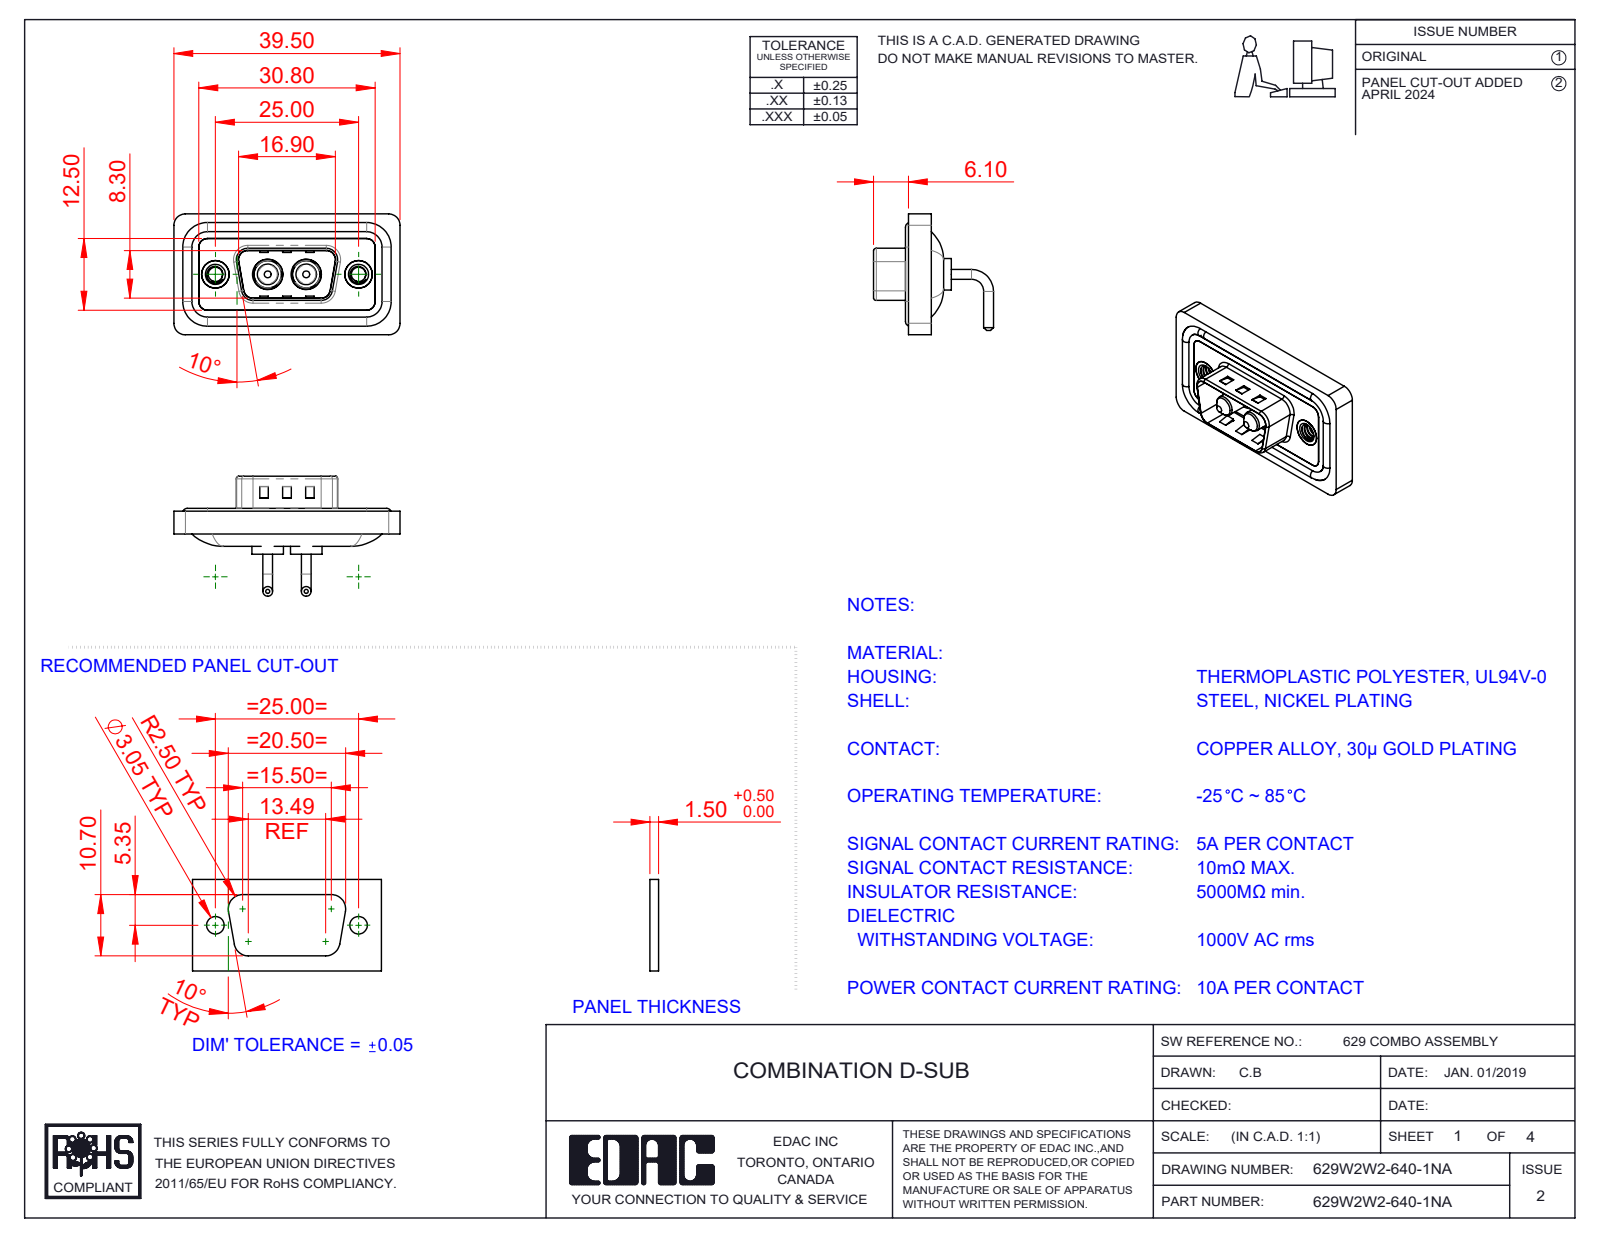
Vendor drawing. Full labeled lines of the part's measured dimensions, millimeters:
Part name (STEP PRODUCT): 629Combo Threaded Rivet_A; 629Combo Housing_2W2; 629Combo Shell Rear_09 Contacts; 629Combo Shell Front_09 Contacts (+3 more)
STEP written by: SolidWorks 2023 (CONFIG_CONTROL_DESIGN)
Units: millimetres
Bodies: 11 solids, 491 faces (165 planar, 220 cylindrical, 106 other)
Overall size (bounding box): 39.5 × 21.1 × 20.95
Volume: 4 472 mm³ · Surface area: 7 069 mm²
Round holes (diameter × count): ⌀2.5 ×2, ⌀4 ×2, ⌀4.8 ×2, ⌀4.85 ×2, ⌀5 ×2, ⌀5.3 ×2
Round bosses / shafts (diameter × count): ⌀1.7 ×4, ⌀1.6 ×4, ⌀5.5 ×2, ⌀5.2 ×2, ⌀4.9 ×2, ⌀4.75 ×2, ⌀3.75 ×2, ⌀3.6 ×2
Partial cylindrical surfaces — rounded edges, fillets, slot ends (radius × count): R1.5 ×18, R2 ×18, R0.5 ×8, R1.6 ×8, R0.25 ×4, R0.6 ×4, R0.65 ×4, R0.9 ×4
Main face-to-face distances: 0.4, 2.9, 1.1, 0.8, 2.1, 2.5, 3.1, 1.6, 4.5, 1.5
Hole centre spacings: 9.14, 15.86, 6.72, 25
